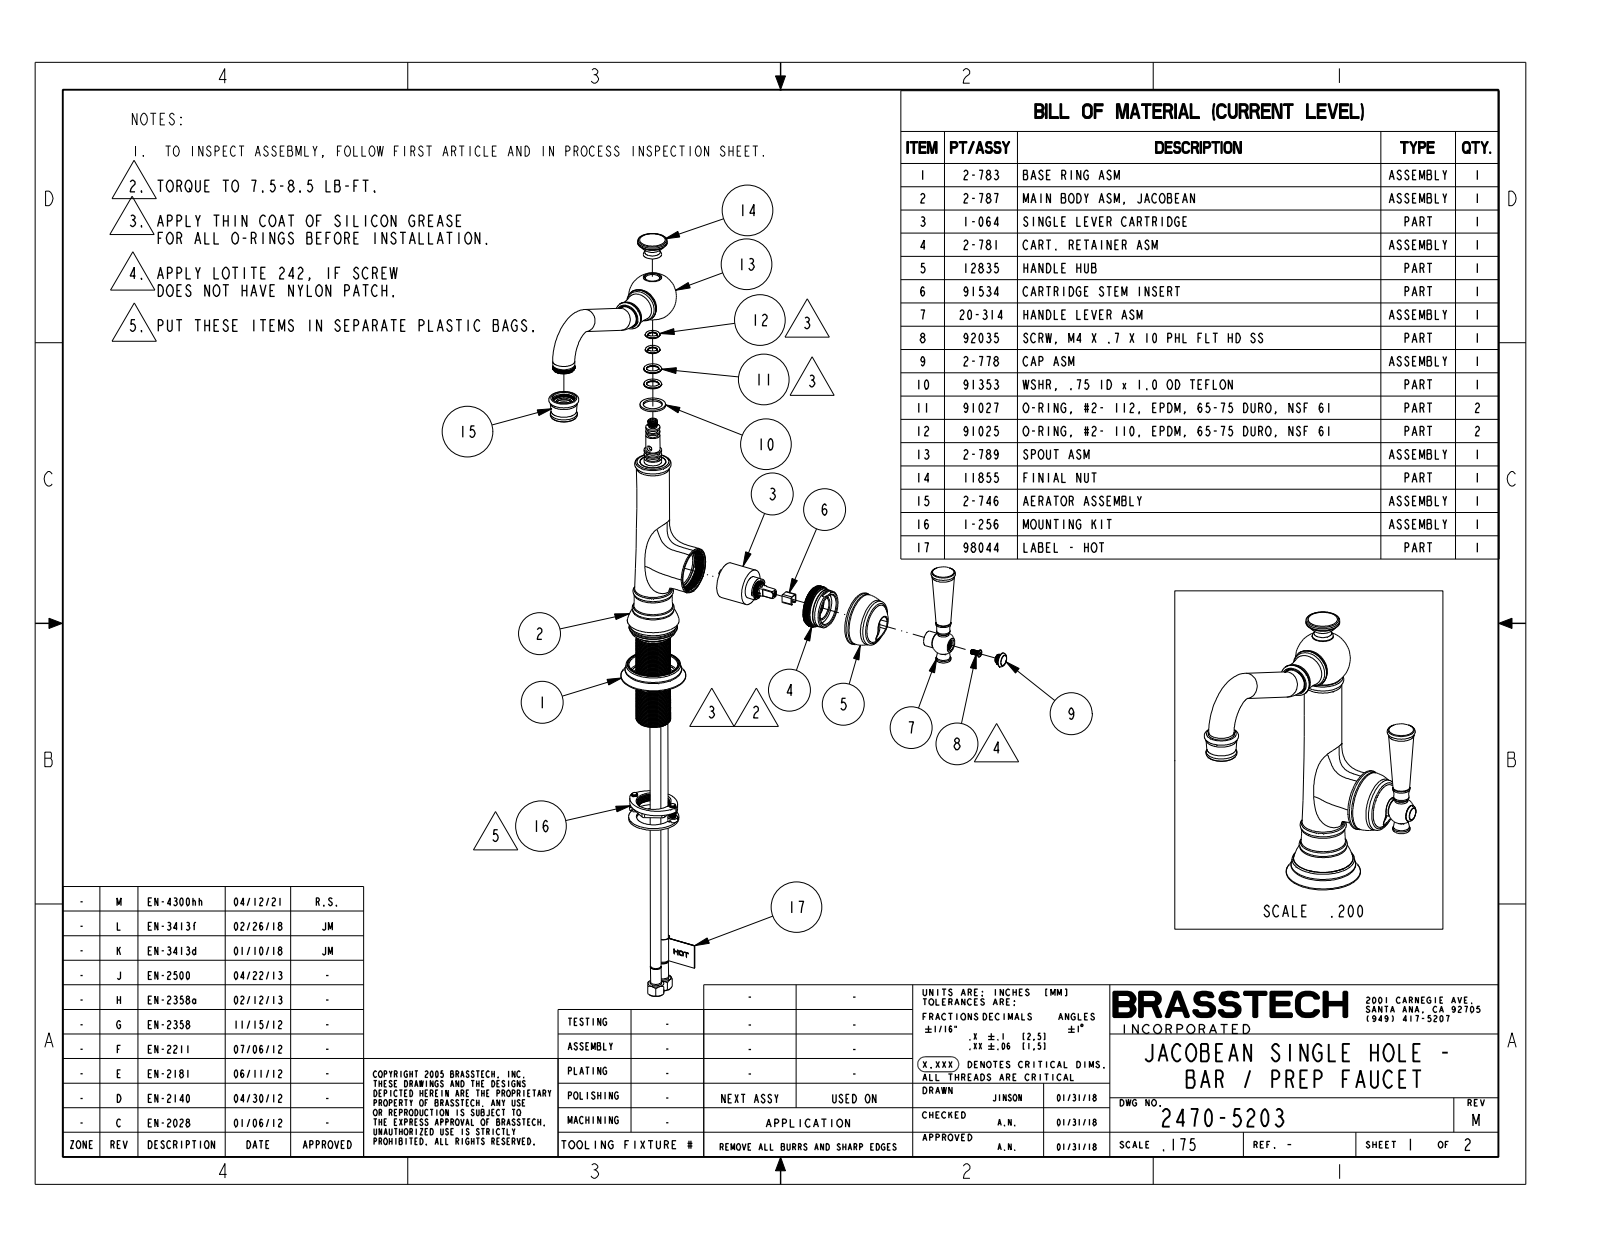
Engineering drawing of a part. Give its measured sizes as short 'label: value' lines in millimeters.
name: 2470-5203
written by: CREO PARAMETRIC BY PTC INC, 2018400 (AUTOMOTIVE_DESIGN)
unit: mm
bodies: 2 solids, 191 faces (16 planar, 22 cylindrical, 153 other)
size: 259.1 × 217.4 × 124.7
volume: 480 100 mm³; area: 66 450 mm²
bosses: 2× ⌀22.1, 1× ⌀51.3, 1× ⌀33.4, 1× ⌀29.5, 1× ⌀28.7, 1× ⌀15.1, 1× ⌀14.2, 1× ⌀14.2
rounds: 2× R8.6
face distances: 194.4, 194.9, 0.6, 196.3, 1.9, 1.3, 24.5, 217.1, 22.7, 22.2
